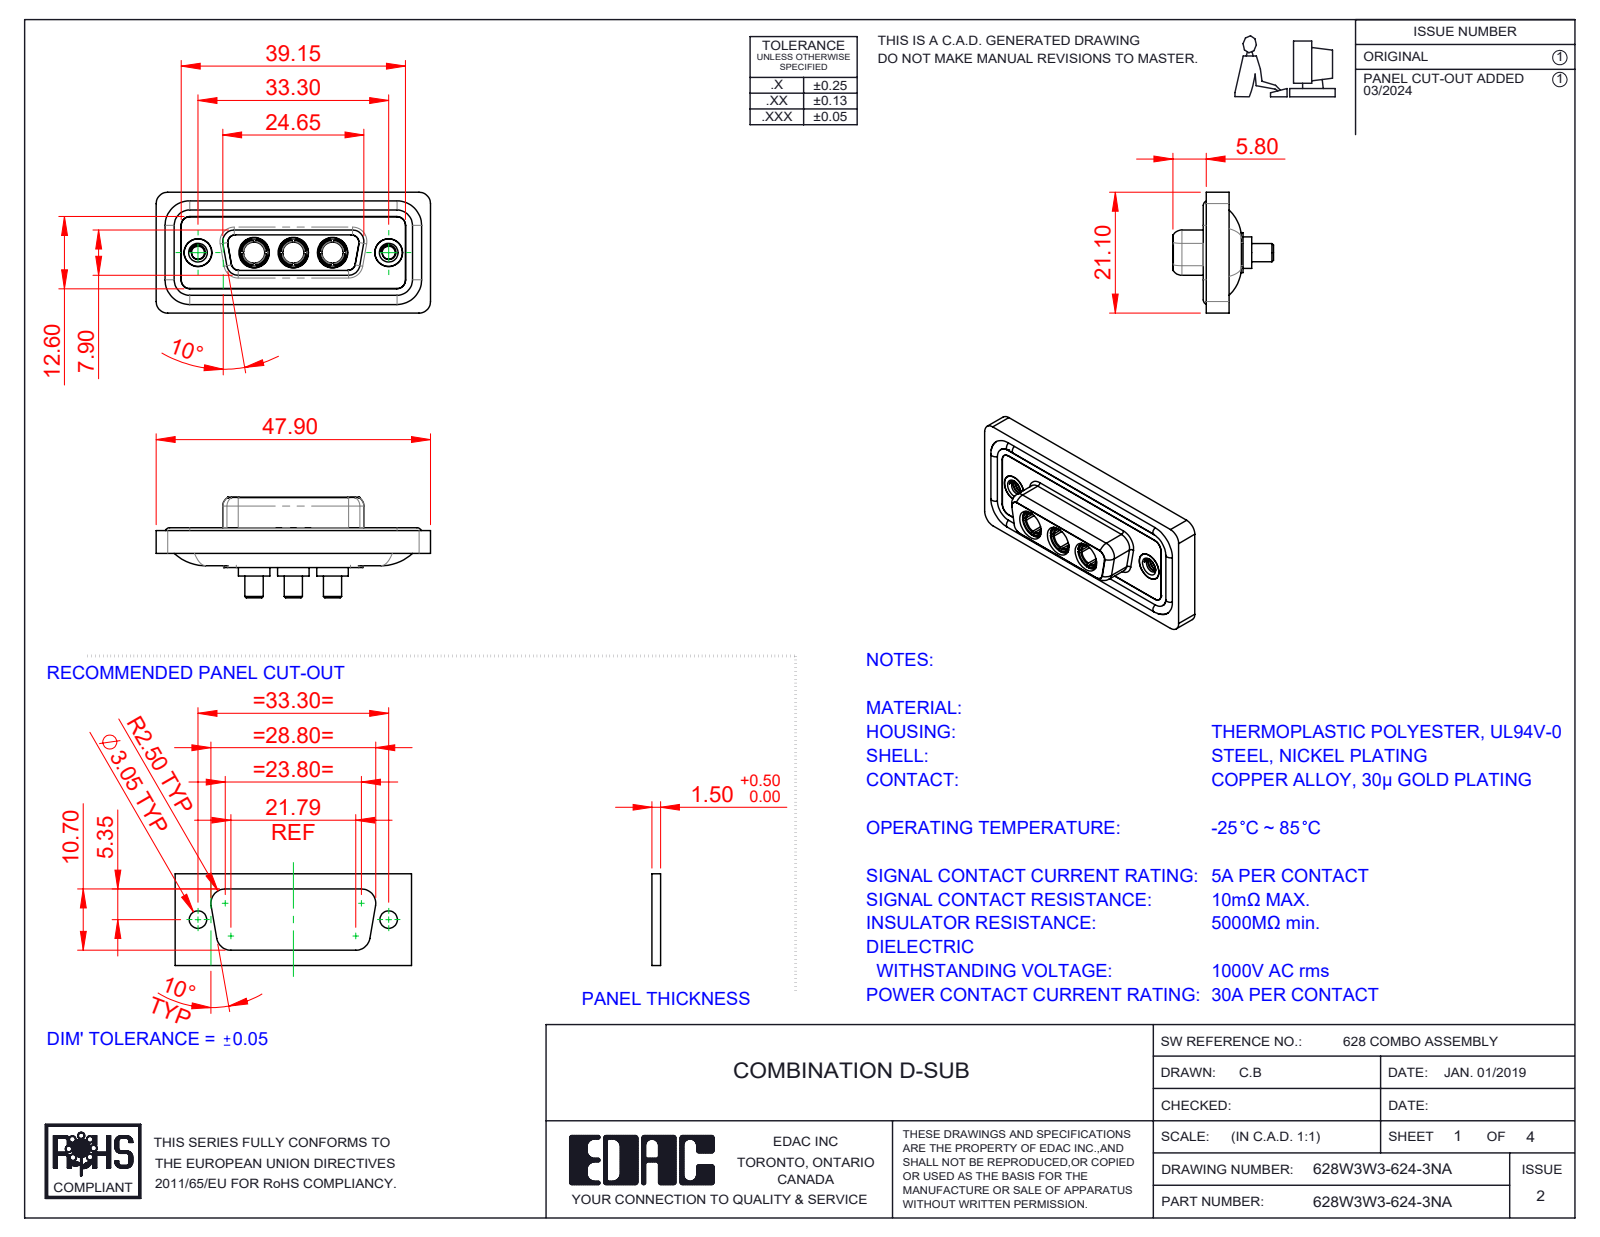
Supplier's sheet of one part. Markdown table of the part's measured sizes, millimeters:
| quantity | value |
| --- | --- |
| part name | 628Combo Threaded Rivet_A; 628Combo Shell Front_15 Contacts; Power Socket_30A S; 628Combo Housing_3W3 (+3 more) |
| STEP written by | SolidWorks 2023 (CONFIG_CONTROL_DESIGN) |
| units | millimeters |
| bodies | 13 solids, 606 faces (192 planar, 259 cylindrical, 155 other) |
| overall size | 47.9 × 21.1 × 17.55 |
| volume | 6 049 mm³ |
| surface area | 9 750 mm² |
| round holes (diameter × count) | 4.85 × 5, 3.7 × 3, 5.3 × 3, 2.26 × 2, 4 × 2, 4.05 × 2, 5 × 2 |
| round bosses / shafts (diameter × count) | 1.6 × 4, 5.5 × 3, 5.2 × 3, 4.96 × 3, 4.75 × 3, 3.75 × 3, 3.2 × 3, 4.95 × 2 |
| partial cylindrical surfaces (radius × count) | 1.5 × 22, 2 × 20, 1.35 × 12, 1.6 × 8, 0.25 × 4, 0.5 × 4, 0.6 × 4, 0.65 × 4 |
| main face-to-face distances | 0.4, 1.8, 1.6, 0.5, 7.45, 1.1, 2.9, 5.65, 7.05, 6.6 |
| hole center spacings | 6.85, 9.8, 16.65, 23.5, 13.7, 33.3 |
